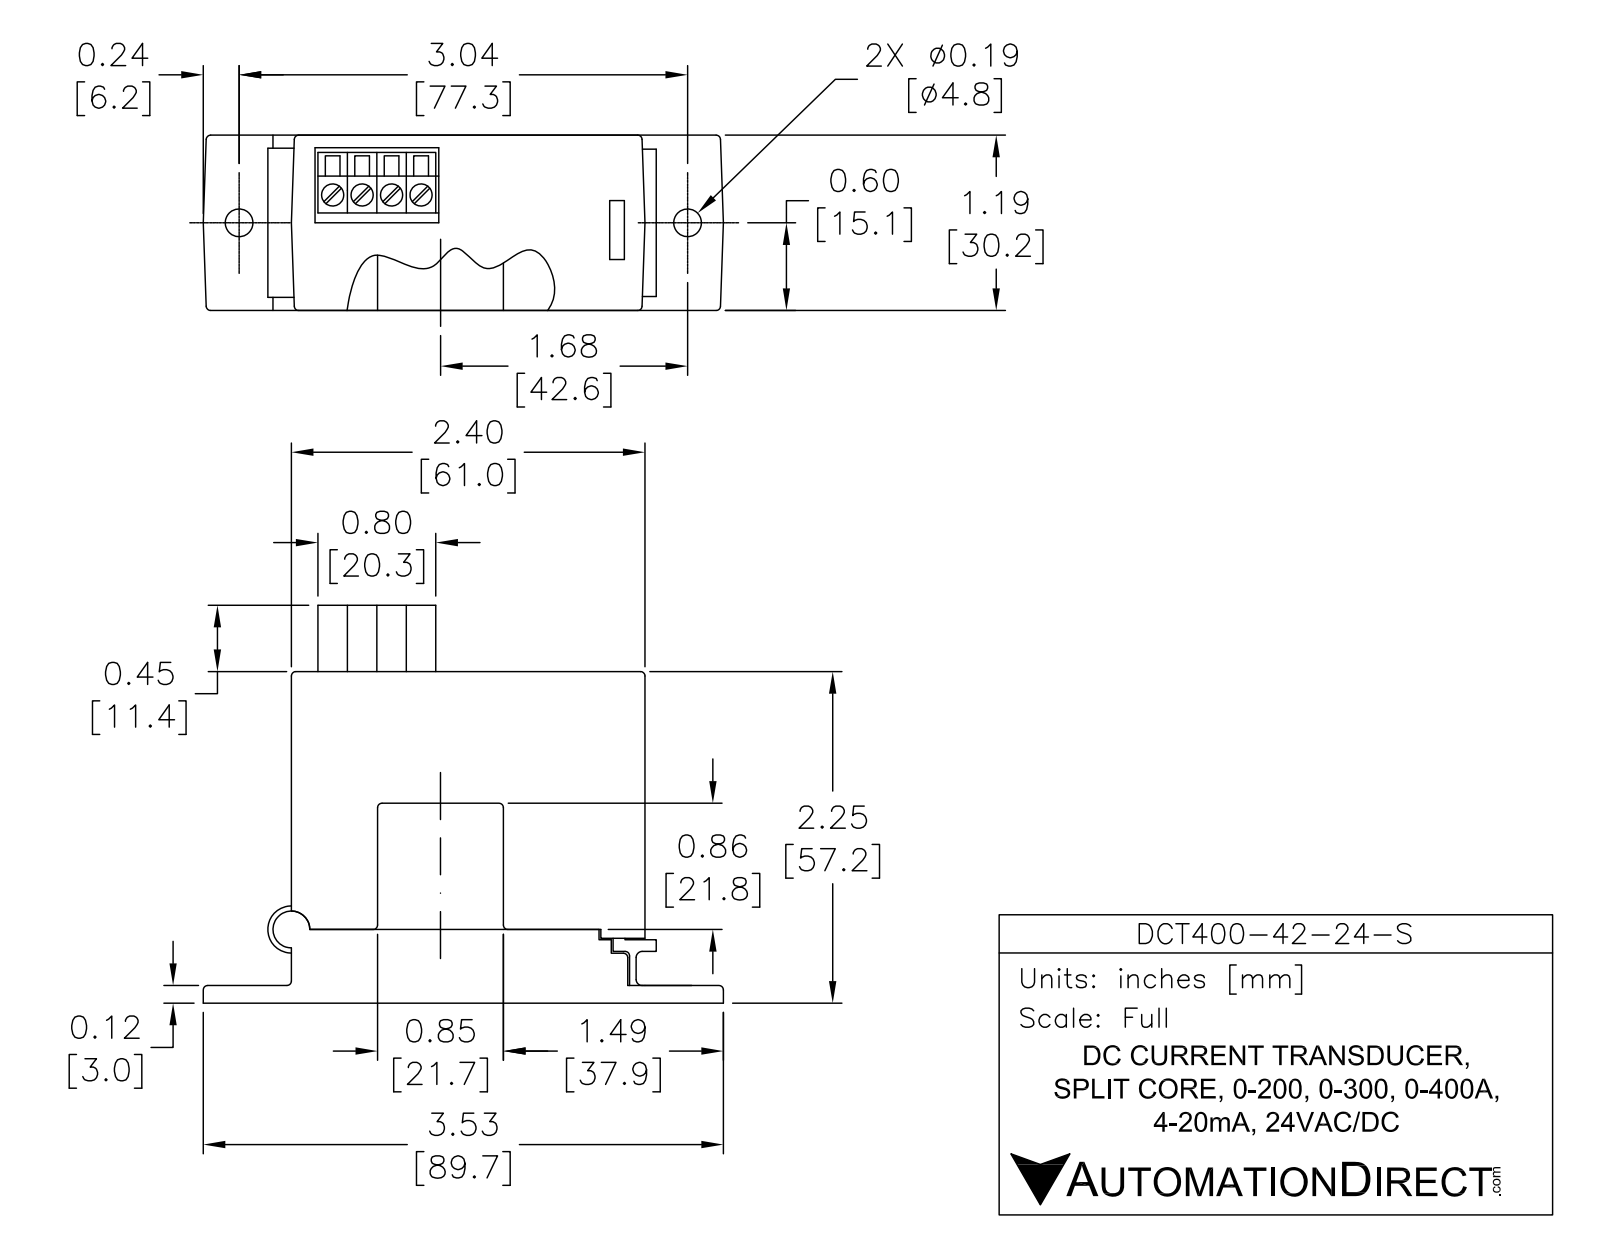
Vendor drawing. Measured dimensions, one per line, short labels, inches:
name: DCT400-42-24-S
written by: SolidWorks 2017 (AUTOMOTIVE_DESIGN)
unit: in
bodies: 4 solids, 158 faces (100 planar, 50 cylindrical, 8 other)
size: 3.531 × 2.7 × 1.189
volume: 5.725 in³; area: 35.03 in²
holes: 4× ⌀0.157, 2× ⌀0.188, 1× ⌀0.26
bosses: 1× ⌀0.25
rounds: 22× R0.03, 1× R0.16, 1× R0.17
face distances: 1.189, 2.252, 0.5, 1.752, 2.399, 0.505, 1.747, 0.118, 0.382, 0.387
hole spacings: 0.197, 0.398, 0.201, 0.596, 0.632, 0.822, 1.019, 1.213
